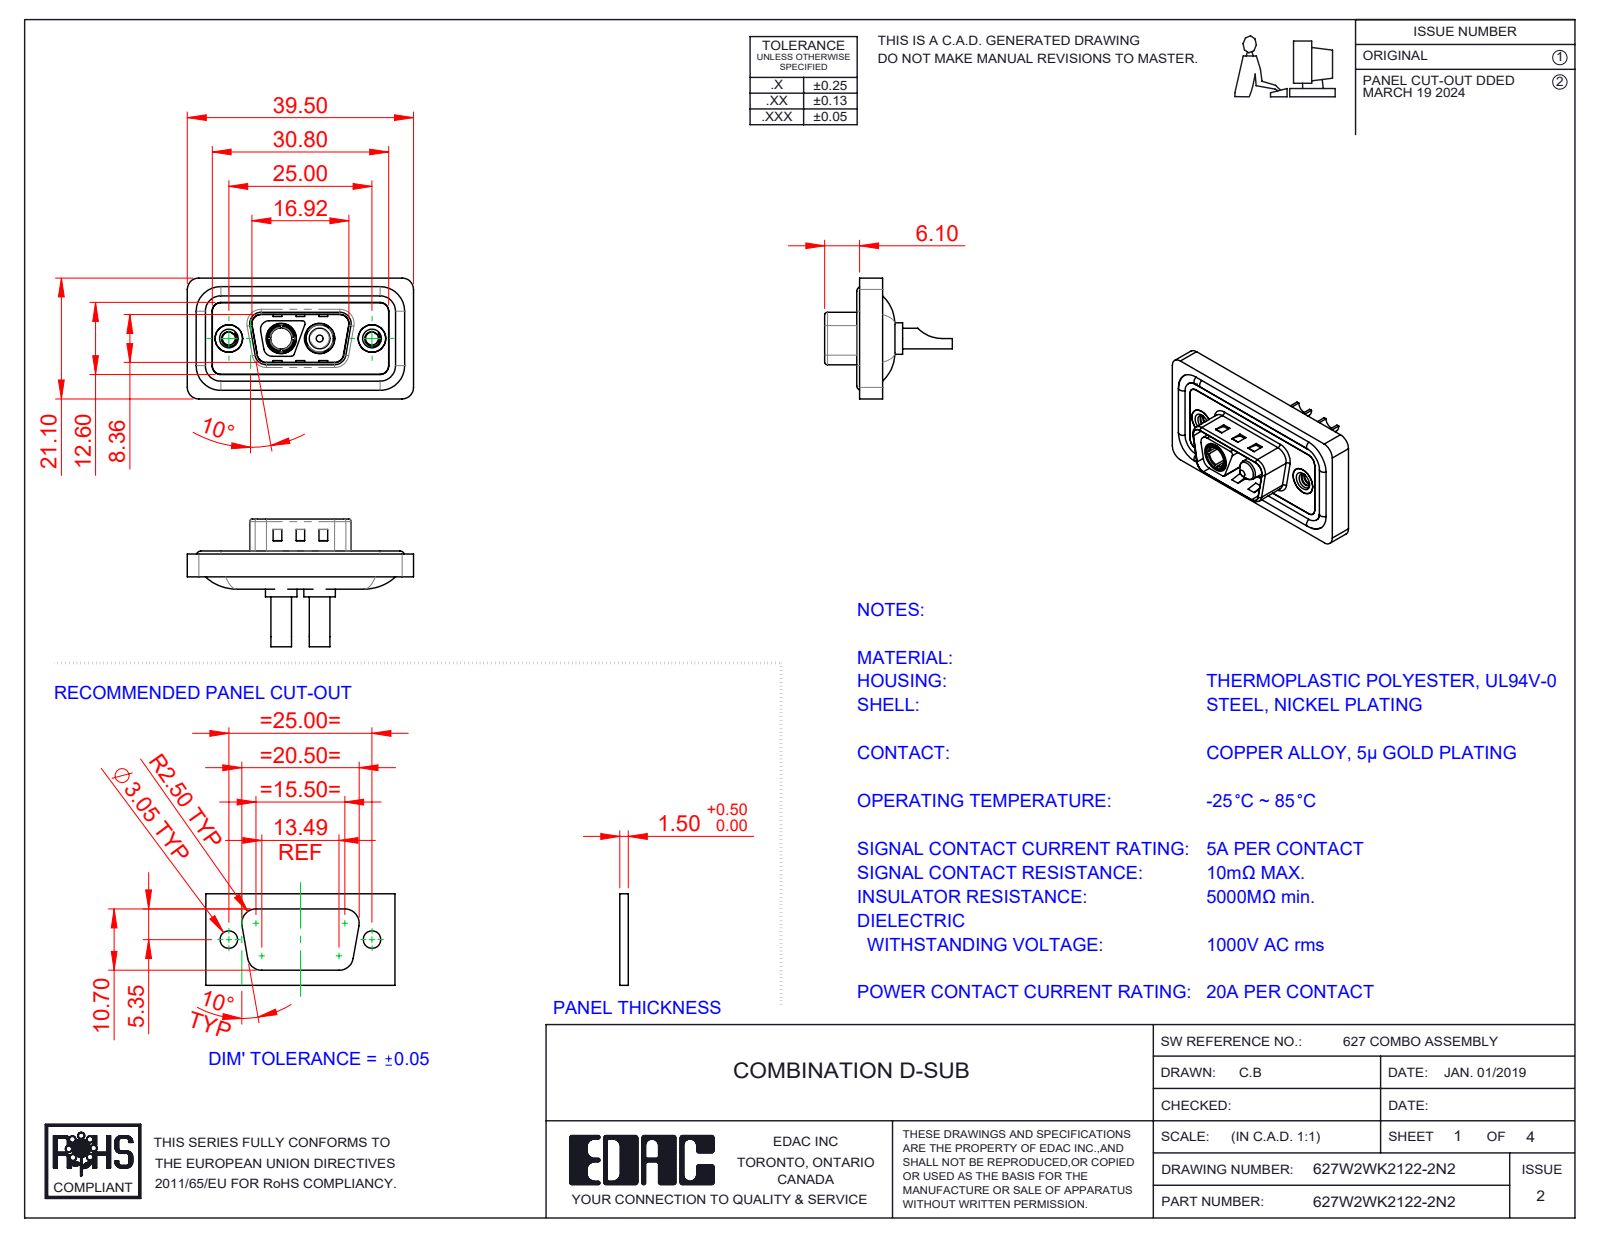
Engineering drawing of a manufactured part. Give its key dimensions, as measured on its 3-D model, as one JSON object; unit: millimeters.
{"part_name": "627W2WK2122-2N2; 627Combo Housing_2WK2; Power Pin_20A SC; 627Combo Shell Front_09 Contacts (+4 more)", "step_written_by": "SolidWorks 2023 (CONFIG_CONTROL_DESIGN)", "units": "millimeters", "bodies": {"solids": 11, "faces": 547, "planar": 195, "cylindrical": 233, "other": 119}, "overall_size": [39.5, 22.3, 21.1], "volume_mm3": 4580, "surface_area_mm2": 7507, "round_holes": [[2.26, 2], [2.7, 2], [4, 2], [4.8, 2], [4.85, 2], [5, 2], [5.3, 2], [3.7, 1]], "round_bosses_or_shafts": [[1.6, 4], [5.5, 2], [5.2, 2], [4.9, 2], [4.75, 2], [3.75, 2], [3.6, 2], [4.96, 1]], "partial_cylinders_radius": [[1.5, 24], [2, 18], [0.5, 10], [1.6, 8], [0.25, 4], [0.6, 4], [0.65, 4], [0.9, 4]], "face_to_face_distances": [0.4, 1.1, 2.9, 0.5, 3.1, 1.6, 1.5, 4, 2.5, 1.8], "hole_center_spacings": [9.14, 15.86, 6.72, 25]}
